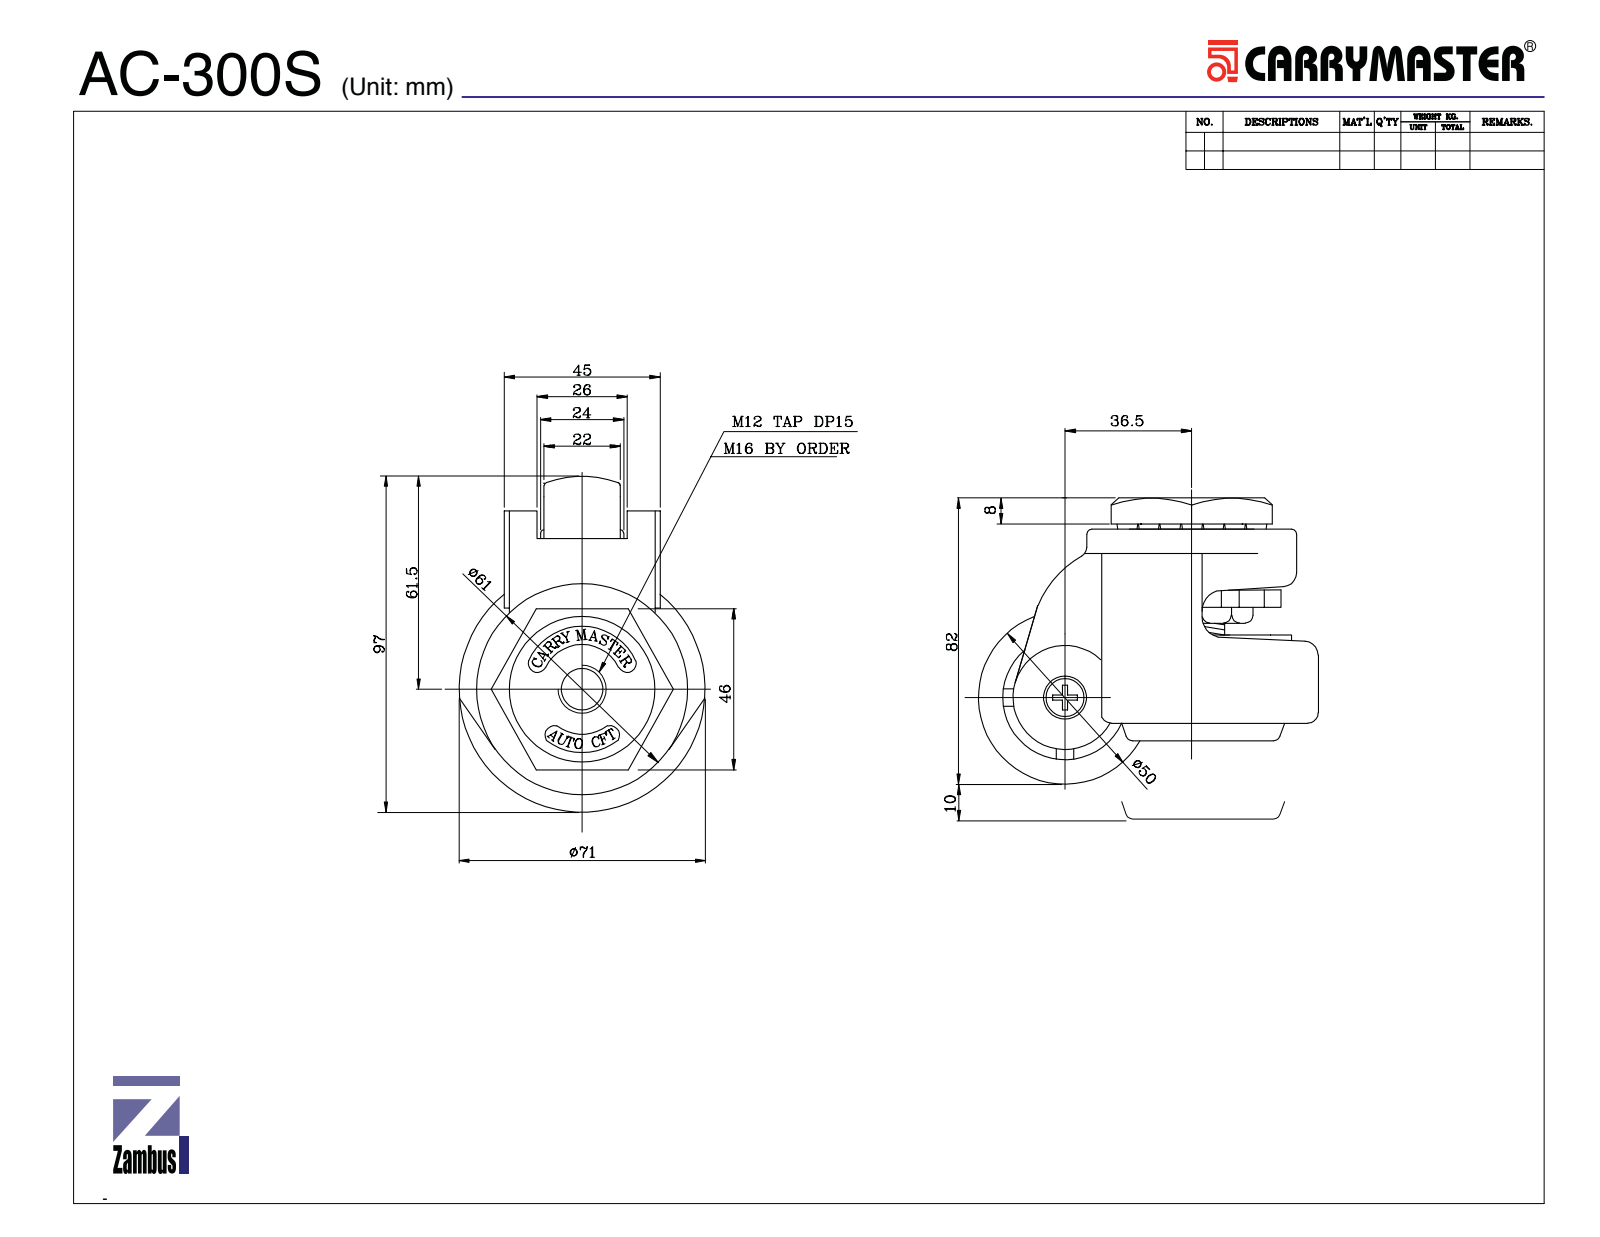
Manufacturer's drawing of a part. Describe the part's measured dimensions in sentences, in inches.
The part is named "AC-300S FOOT MOUNT; AC-300S ASSY R1; AC-300S FOOT MOUNT(RUBBER); AC-300 FRAME (+8 more)". Its 3-D file was written by "SolidWorks 2016 (CONFIG_CONTROL_DESIGN)". It is 46 solids with 1604 faces: 439 planar, 301 cylindrical and 864 other. Overall it measures 3.878 by 3.237 by 2.772 inches. Its volume is 11.96 cubic inches and its surface area 128.4 square inches. Round holes: 1 of diameter 0.098, 1 of diameter 0.138, 1 of diameter 0.268, 1 of diameter 0.335, 1 of diameter 0.339, 1 of diameter 0.398, 1 of diameter 0.402, 1 of diameter 0.689, 1 of diameter 0.709, 1 of diameter 1.102, 1 of diameter 1.417, 1 of diameter 1.575. Round bosses or shafts: 2 of diameter 0.748, 2 of diameter 0.394, 2 of diameter 0.315, 1 of diameter 2.283, 1 of diameter 1.622, 1 of diameter 1.496, 1 of diameter 0.984, 1 of diameter 0.925. Partial cylindrical surfaces (rounded edges, fillets, slot ends): 64 of radius 0.039, 16 of radius 0.079, 13 of radius 0.118, 9 of radius 0.197, 6 of radius 0.098, 4 of radius 0.02, 4 of radius 0.059, 2 of radius 0.096. The main face-to-face distances are 0.394, 0.787, 0.138, 0.197, 0.591, 0.276, 1.772, 1.181, 0.444, 1.063.
